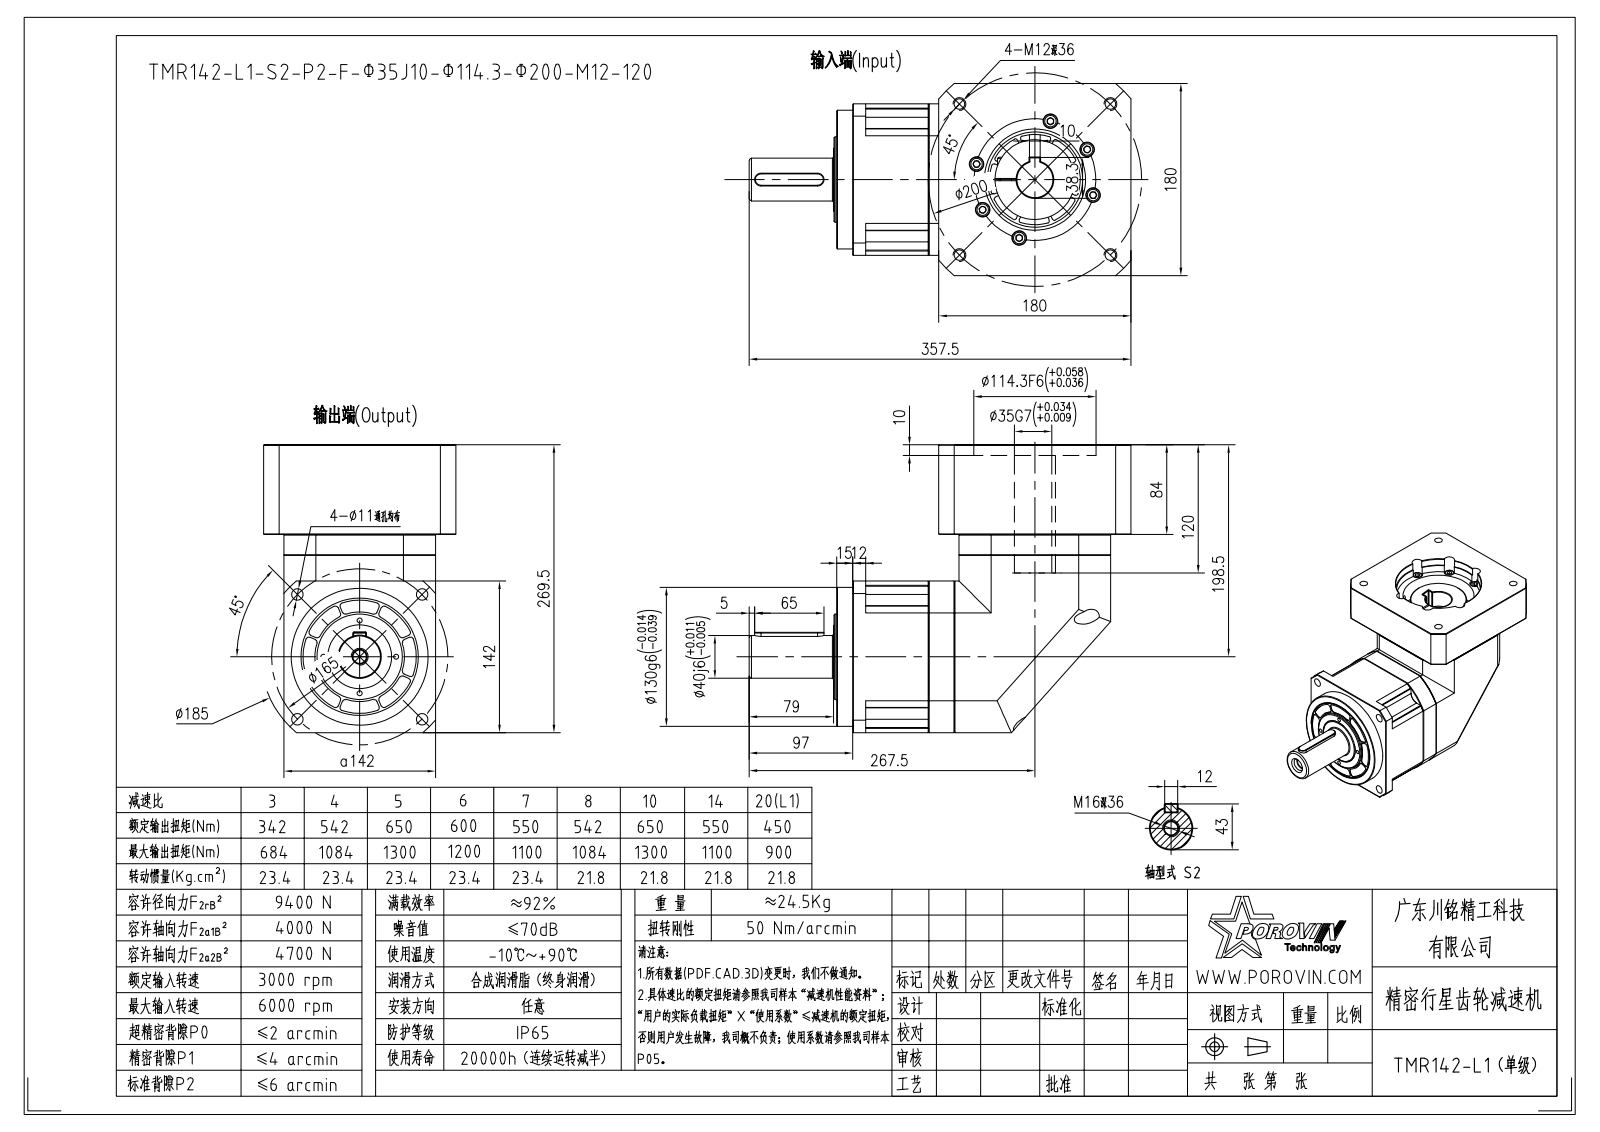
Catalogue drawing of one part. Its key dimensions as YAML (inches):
part_name: "SPRING_LOCK_WASHERS--NORMAL_TYP; HEXAGON_SOCKET_HEAD_CAP_S-15493; HEXAGON_SOCKET_HEAD_CAP_S-24392; HEXAGON_SOCKET_HEAD_CAP_S-25544 (+8 more)"
step_written_by: "CREO PARAMETRIC BY PTC INC, 2020053 (CONFIG_CONTROL_DESIGN)"
units: inches
bodies: {solids: 42, faces: 1360, planar: 536, cylindrical: 557, other: 267}
overall_size: [14.075, 10.61, 7.087]
volume: 414.6
surface_area: 894.2
round_holes:
  - {diameter: 0.342, count: 16}
  - {diameter: 0.354, count: 16}
  - {diameter: 0.551, count: 16}
  - {diameter: 0.268, count: 13}
  - {diameter: 0.197, count: 4}
  - {diameter: 0.402, count: 4}
  - {diameter: 0.433, count: 4}
  - {diameter: 0.335, count: 1}
  - {diameter: 0.413, count: 1}
  - {diameter: 0.535, count: 1}
  - {diameter: 0.669, count: 1}
  - {diameter: 0.689, count: 1}
round_bosses_or_shafts:
  - {diameter: 0.512, count: 16}
  - {diameter: 0.507, count: 16}
  - {diameter: 0.315, count: 16}
  - {diameter: 5.118, count: 1}
  - {diameter: 4.921, count: 1}
  - {diameter: 3.15, count: 1}
  - {diameter: 2.953, count: 1}
  - {diameter: 2.638, count: 1}
partial_cylinders:
  - {radius: 0.079, count: 64}
  - {radius: 0.039, count: 20}
  - {radius: 0.413, count: 4}
  - {radius: 0.236, count: 3}
  - {radius: 3.228, count: 3}
  - {radius: 1.673, count: 2}
  - {radius: 0.325, count: 1}
  - {radius: 1.969, count: 1}
face_to_face_distances: [0.748, 6.339, 5.591, 0.965, 0.957, 0.768, 7.087, 4.075, 3.307, 0.591]
hole_center_spacings: [2.224, 1.702, 2.474, 3.146, 4.11, 4.333, 0.833, 1.835]
